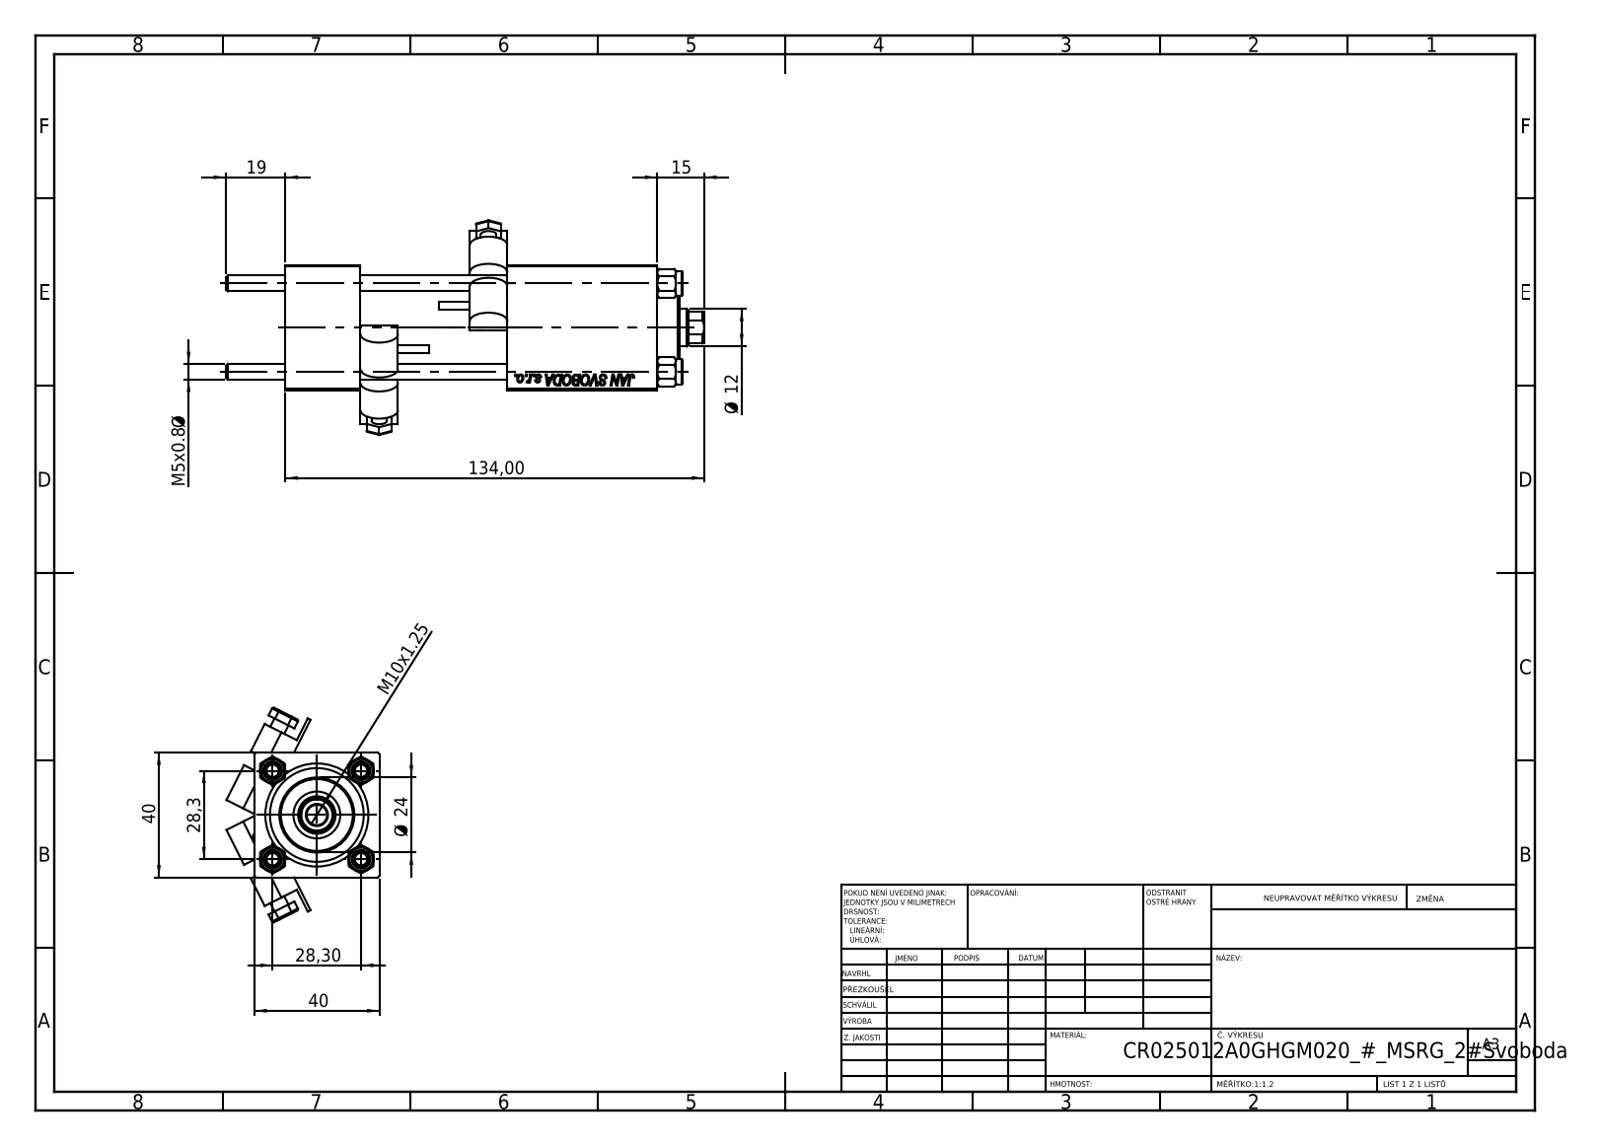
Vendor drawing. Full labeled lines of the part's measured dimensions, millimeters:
Part name (STEP PRODUCT): V215CR_BODY_A; MSRF_MSRG1; CR025_012_A_0_G_A_G_M_020_+#_##_TYCINKA; V215CR_VCP (+2 more)
STEP written by: SolidWorks 2019 (CONFIG_CONTROL_DESIGN)
Units: millimetres
Bodies: 13 solids, 1195 faces (553 planar, 106 cylindrical, 536 other)
Overall size (bounding box): 153 × 68.71 × 48.93
Volume: 151 725 mm³ · Surface area: 63 023 mm²
Round holes (diameter × count): ⌀5 ×4, ⌀20 ×3, ⌀7 ×2, ⌀13.16 ×2, ⌀6.5 ×1, ⌀12 ×1, ⌀15 ×1, ⌀25 ×1, ⌀30 ×1
Round bosses / shafts (diameter × count): ⌀8 ×4, ⌀5 ×2, ⌀2.5 ×2, ⌀31 ×1, ⌀24 ×1
Partial cylindrical surfaces — rounded edges, fillets, slot ends (radius × count): R0.5 ×12, R6 ×4, R5.5 ×1
Main face-to-face distances: 40, 24, 71, 47, 95, 119, 48, 90.3, 66.3, 19.3
Hole centre spacings: 20.01, 28.3, 40.02, 72
